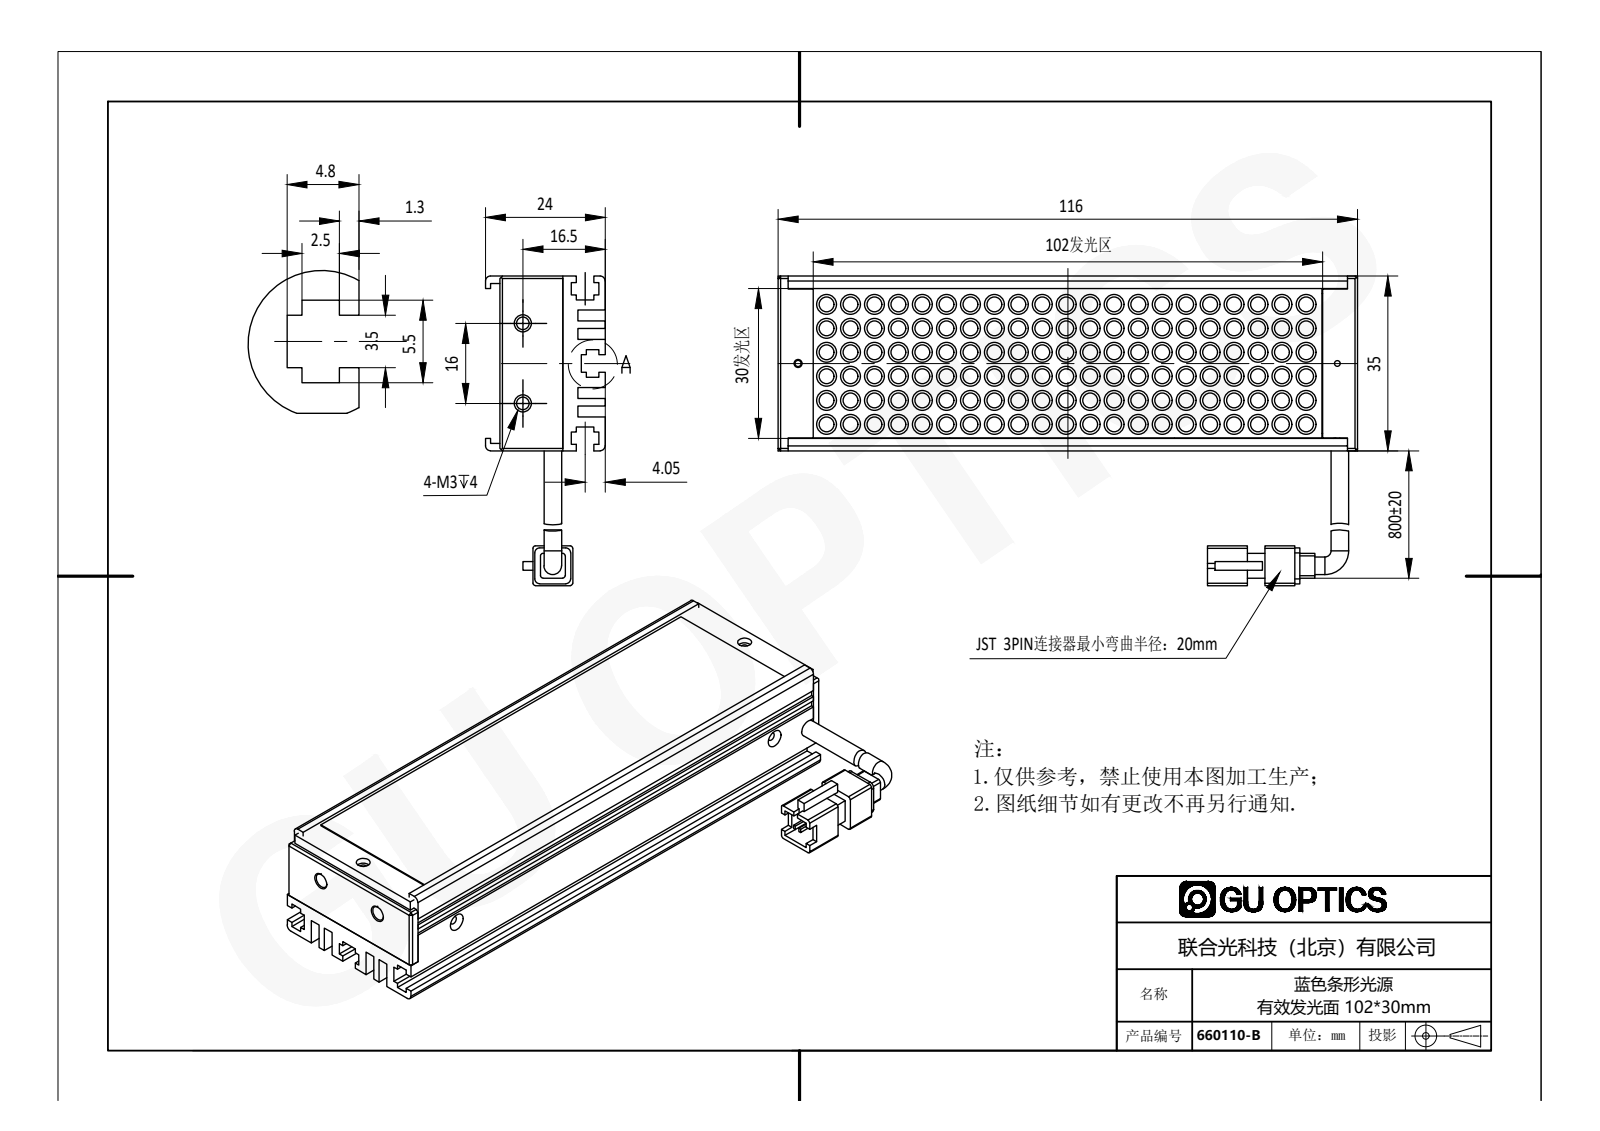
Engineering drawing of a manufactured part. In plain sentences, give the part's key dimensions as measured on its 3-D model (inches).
The part is named "660110-B". Its 3-D file was written by "SolidWorks 2016 (AUTOMOTIVE_DESIGN)". It is 8 solids with 1209 faces: 393 planar, 587 cylindrical and 229 other. Overall it measures 4.567 by 2.441 by 0.945 inches. Its volume is 3.279 cubic inches and its surface area 93.18 square inches. Round holes: 5 of diameter 0.063, 2 of diameter 0.059, 2 of diameter 0.067, 2 of diameter 0.098, 2 of diameter 0.11, 2 of diameter 0.118, 1 of diameter 0.043, 1 of diameter 0.049, 1 of diameter 0.079. Round bosses or shafts: 126 of diameter 0.157, 126 of diameter 0.118, 2 of diameter 0.138. Partial cylindrical surfaces (rounded edges, fillets, slot ends): 12 of radius 0.039, 8 of radius 0.02, 1 of radius 0.065. The main face-to-face distances are 0.079, 0.087, 0.339, 0.039, 0.098, 0.496, 0.575, 0.354, 0.157, 0.276. The hole center spacings are 4.252, 0.276, 0.36, 0.413, 3.898, 3.904, 4.261, 0.63.
